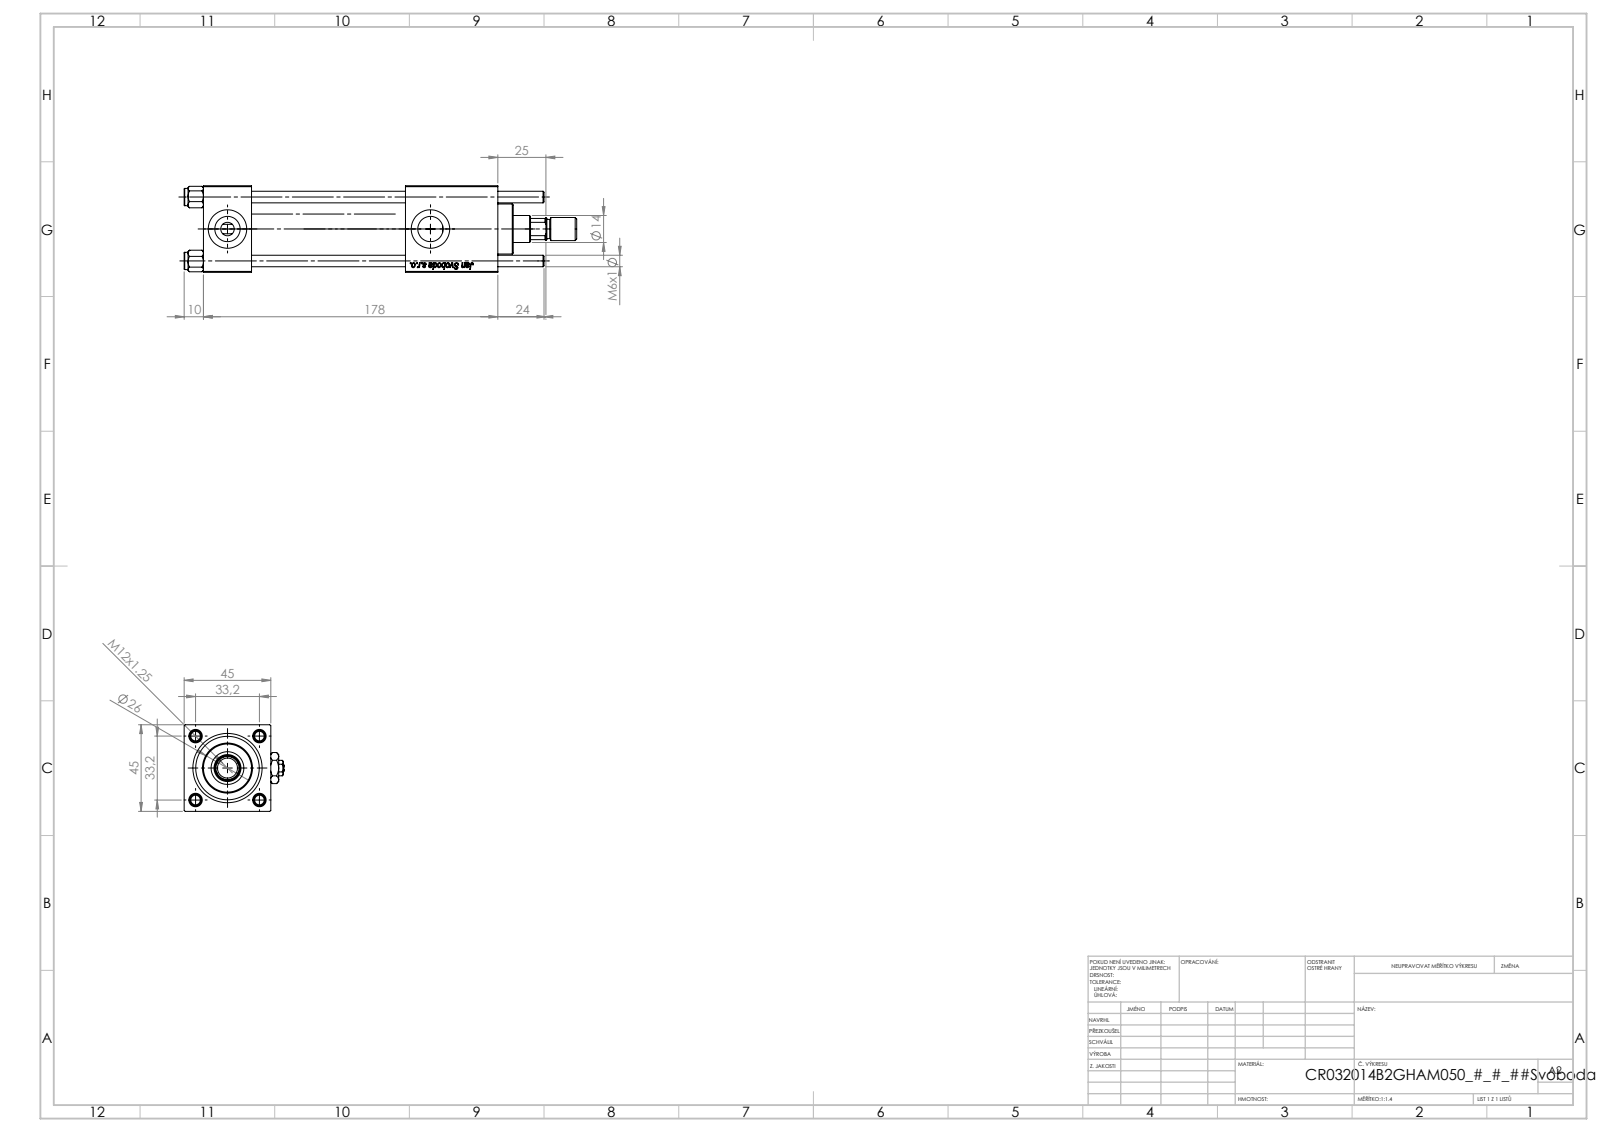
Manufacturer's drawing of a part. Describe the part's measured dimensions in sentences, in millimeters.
The part is named "Zatka_pro_OIL_PORT; V215_VC_A; V215CR_B-1; V215CR_B_TYCINKA (+3 more)". Its 3-D file was written by "SolidWorks 2019 (CONFIG_CONTROL_DESIGN)". It is 13 solids with 1222 faces: 458 planar, 88 cylindrical and 676 other. Overall it measures 204 by 52 by 45 millimeters. Its volume is 217 155 cubic millimeters and its surface area 84 679 square millimeters. Round holes: 4 of diameter 6, 2 of diameter 7, 2 of diameter 13.16, 2 of diameter 20, 1 of diameter 6.5, 1 of diameter 14, 1 of diameter 17, 1 of diameter 24, 1 of diameter 32, 1 of diameter 33. Round bosses or shafts: 4 of diameter 9, 1 of diameter 38, 1 of diameter 26, 1 of diameter 12, 1 of diameter 10. Partial cylindrical surfaces (rounded edges, fillets, slot ends): 1 of radius 6.5. The main face-to-face distances are 45, 25, 153, 128, 105, 80, 48, 124.3, 99.3, 19.3. The hole center spacings are 23.48, 33.2, 46.95, 105.5.
